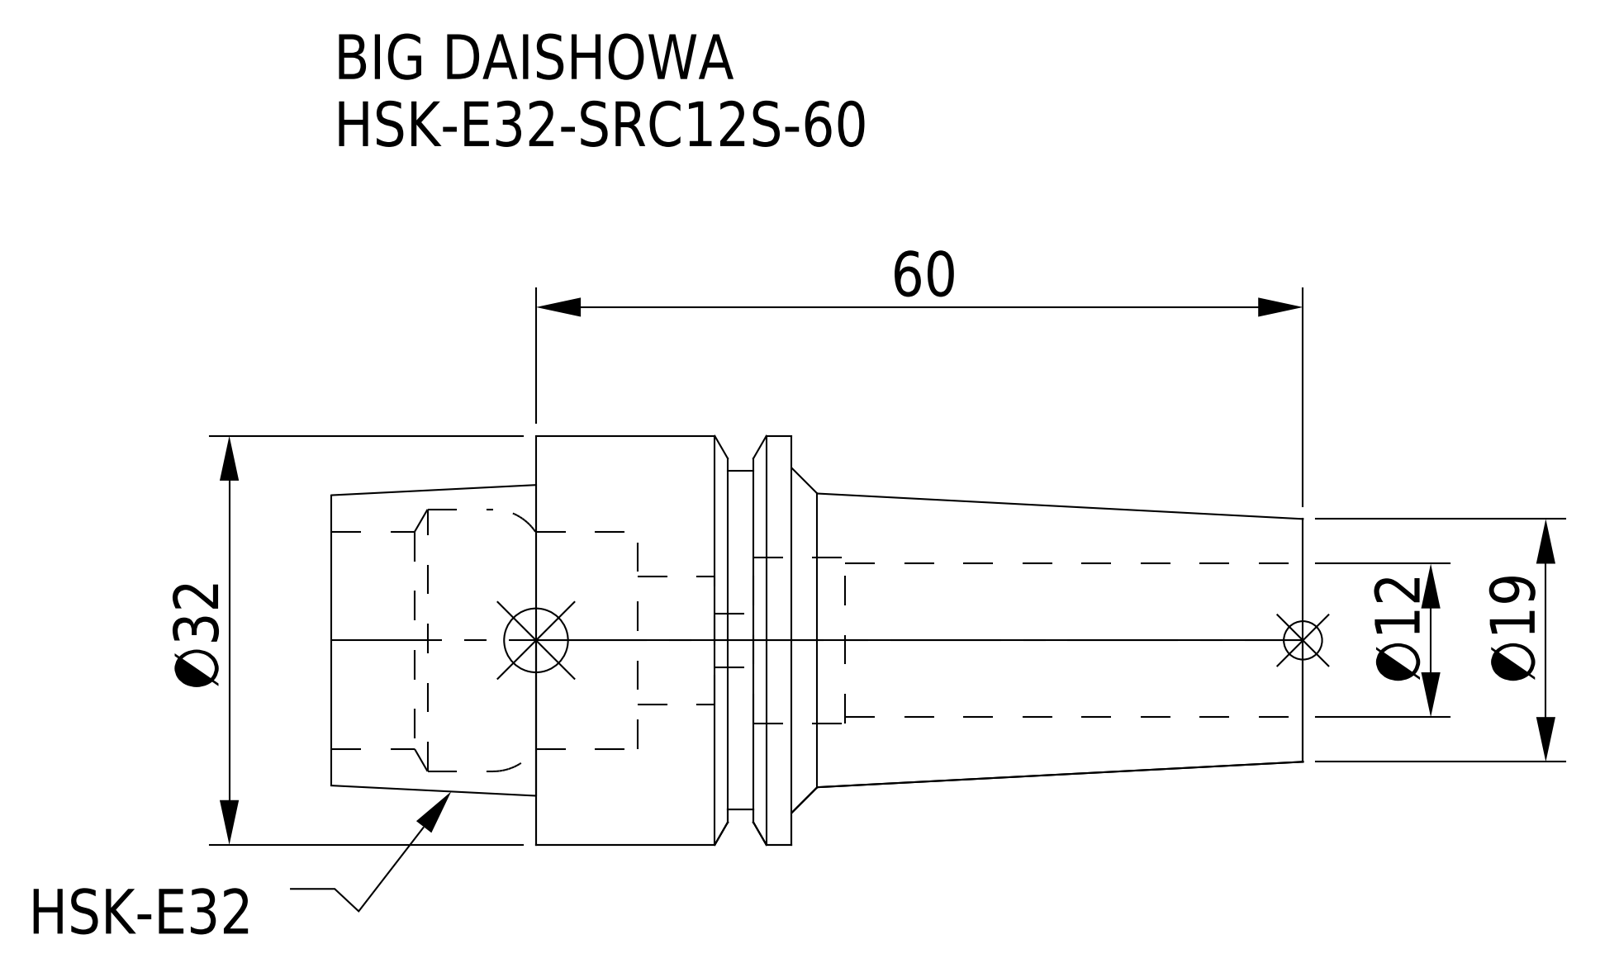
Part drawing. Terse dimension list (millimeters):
name: HSK-E32-SRC12S-60
written by: CREO PARAMETRIC BY PTC INC, 2016380 (AUTOMOTIVE_DESIGN)
unit: mm
bodies: 1 solid, 46 faces (10 planar, 22 cylindrical, 14 other)
size: 76 × 32 × 32
volume: 24 763 mm³; area: 10 848 mm²
holes: 1× ⌀4.2, 1× ⌀10, 1× ⌀12, 1× ⌀13, 1× ⌀17, 1× ⌀20.5
bosses: 1× ⌀32, 1× ⌀26.5
face distances: 20, 3, 17, 36, 33, 16, 40, 43, 60, 76
